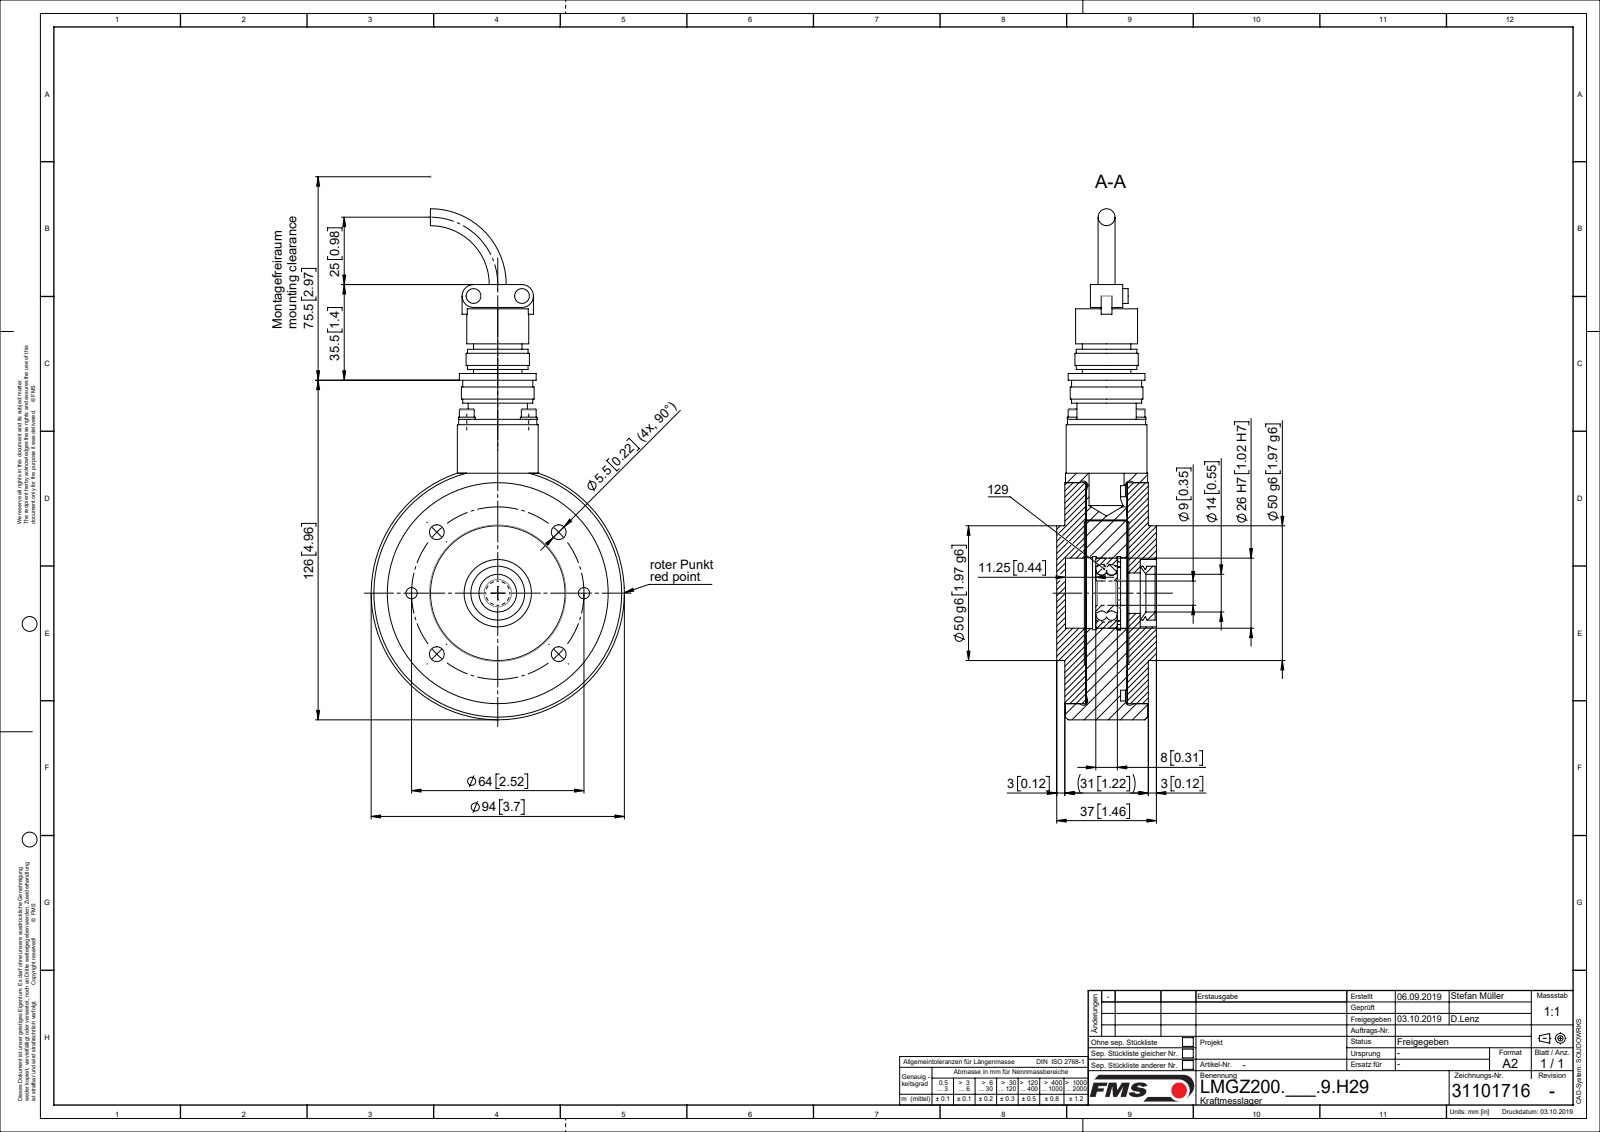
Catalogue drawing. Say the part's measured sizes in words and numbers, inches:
The part is named "L50003; L4900504; L49012; TEIL1 (+8 more)". Its 3-D file was written by "Mechanical Desktop 2007 (CONFIG_CONTROL_DESIGN)". It is 20 solids with 389 faces: 114 planar, 231 cylindrical and 44 other. Overall it measures 7.467 by 3.701 by 1.457 inches. Its volume is 14.71 cubic inches and its surface area 136.6 square inches. Round holes: 6 of diameter 0.217, 4 of diameter 0.102, 4 of diameter 0.126, 4 of diameter 0.134, 4 of diameter 0.17, 4 of diameter 0.26, 2 of diameter 0.394, 1 of diameter 0.354, 1 of diameter 0.551, 1 of diameter 0.591, 1 of diameter 0.634, 1 of diameter 0.906. Round bosses or shafts: 6 of diameter 0.217, 4 of diameter 0.244, 4 of diameter 0.118, 4 of diameter 0.098, 2 of diameter 0.315, 2 of diameter 0.197, 1 of diameter 3.701, 1 of diameter 3.228. Partial cylindrical surfaces (rounded edges, fillets, slot ends): 2 of radius 0.167, 2 of radius 0.315. The main face-to-face distances are 0.6, 0.591, 0.915, 0.906, 0.315, 0.305, 0.61, 0.02, 0.285, 0.433. The hole center spacings are 1.26, 0.64, 0.906, 0.964, 1.782, 2.328, 2.471, 0.491.
